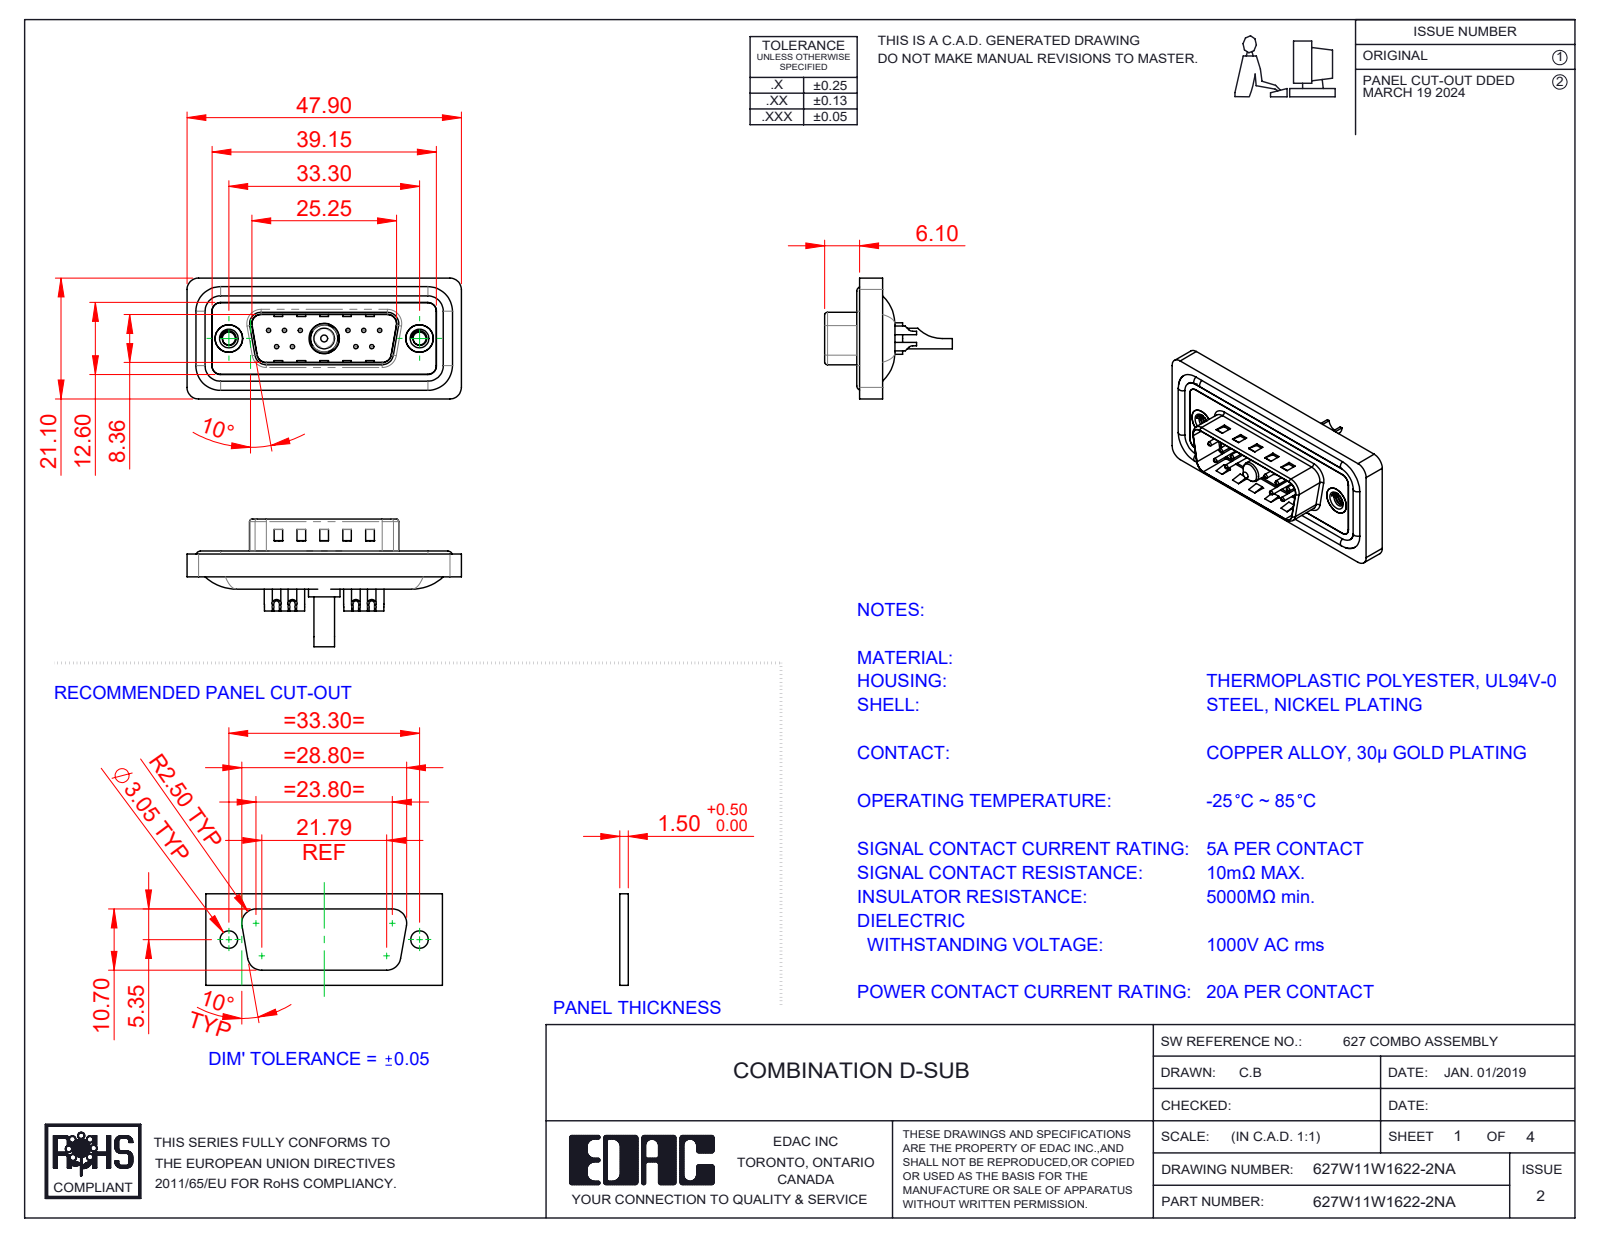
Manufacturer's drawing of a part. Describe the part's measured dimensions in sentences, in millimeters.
The part is named "627Combo Housing_11W1; 627Combo Waterproof Housing_15 Contacts; 627Combo Shell Front_15 Contacts; 627Combo Threaded Rivet_A (+5 more)". Its 3-D file was written by "SolidWorks 2023 (CONFIG_CONTROL_DESIGN)". It is 19 solids with 874 faces: 289 planar, 372 cylindrical and 213 other. Overall it measures 47.9 by 22.3 by 21.1 millimeters. Its volume is 5 478 cubic millimeters and its surface area 8 996 square millimeters. Round holes: 10 of diameter 0.75, 10 of diameter 1, 10 of diameter 1.6, 10 of diameter 2, 2 of diameter 2.26, 2 of diameter 4, 2 of diameter 4.8, 2 of diameter 5, 1 of diameter 2.7, 1 of diameter 4.85, 1 of diameter 5.3. Round bosses or shafts: 10 of diameter 1.5, 4 of diameter 1.6, 2 of diameter 4.9, 1 of diameter 5.5, 1 of diameter 5.2, 1 of diameter 4.75, 1 of diameter 3.75, 1 of diameter 3.6. Partial cylindrical surfaces (rounded edges, fillets, slot ends): 26 of radius 1.5, 20 of radius 2, 9 of radius 1, 8 of radius 0.5, 8 of radius 1.6, 4 of radius 0.25, 4 of radius 0.6, 4 of radius 0.65. The main face-to-face distances are 0.4, 1.1, 1.6, 1.5, 0.5, 2.9, 3.1, 2.5, 4.1, 0.82. The hole center spacings are 3.16, 2.77, 13.85, 11.08, 16.62, 5.03, 5.04, 5.54.
